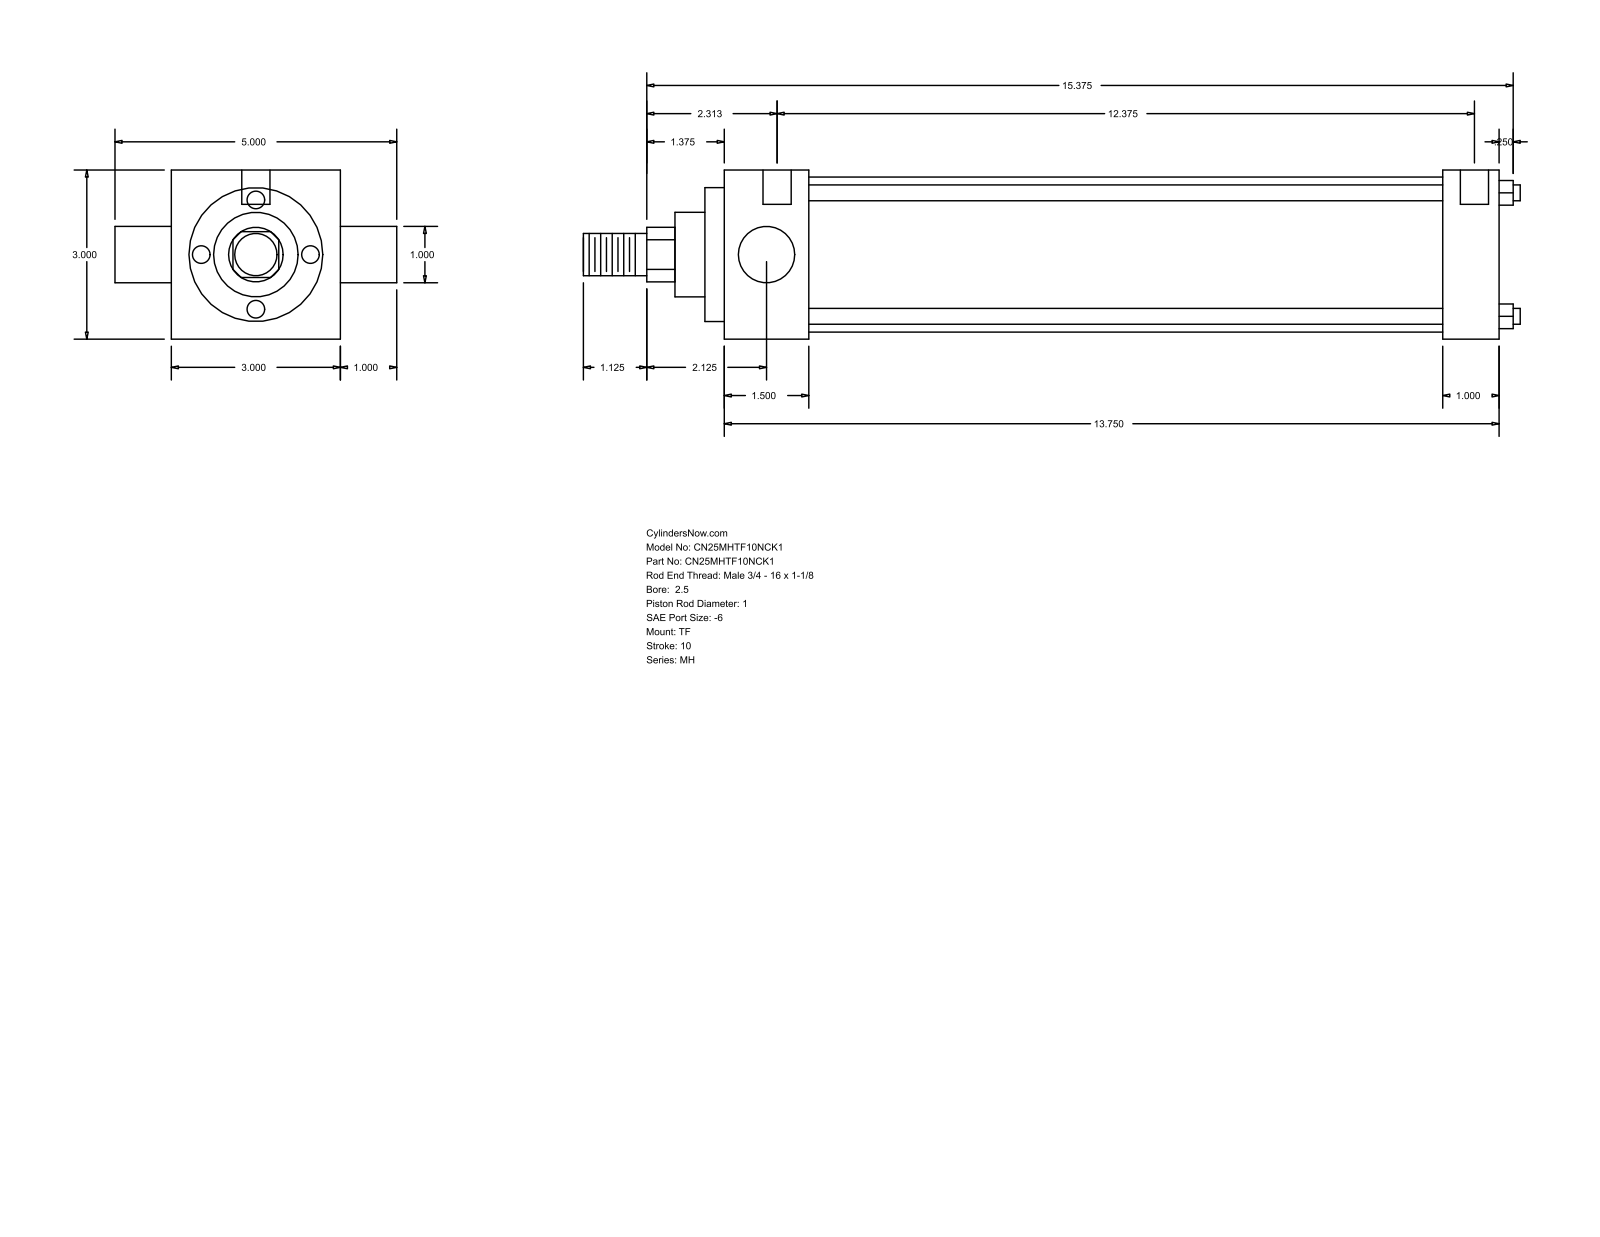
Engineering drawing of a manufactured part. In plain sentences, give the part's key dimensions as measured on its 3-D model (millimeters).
The part is named "MH_TF__0250_1". Its 3-D file was written by "GSSL Pune (CONFIG_CONTROL_DESIGN)". It is 0 solids with 86 faces: 61 planar, 25 cylindrical and 0 other. Overall it measures 422.27 by 127 by 76.2 millimeters. Round holes: 3 of diameter 5.56, 2 of diameter 12.7. Round bosses or shafts: 4 of diameter 7.14, 2 of diameter 25.4, 1 of diameter 69.85, 1 of diameter 60.33, 1 of diameter 38.1, 1 of diameter 19.05. Partial cylindrical surfaces (rounded edges, fillets, slot ends): 1 of radius 12.29. The main face-to-face distances are 76.2, 349.26, 38.11, 311.15, 323.85, 285.74, 25.41, 8.73, 46.84, 332.58. The hole center spacings are 3.18, 4.76, 314.32, 317.5, 319.08, 322.26.
